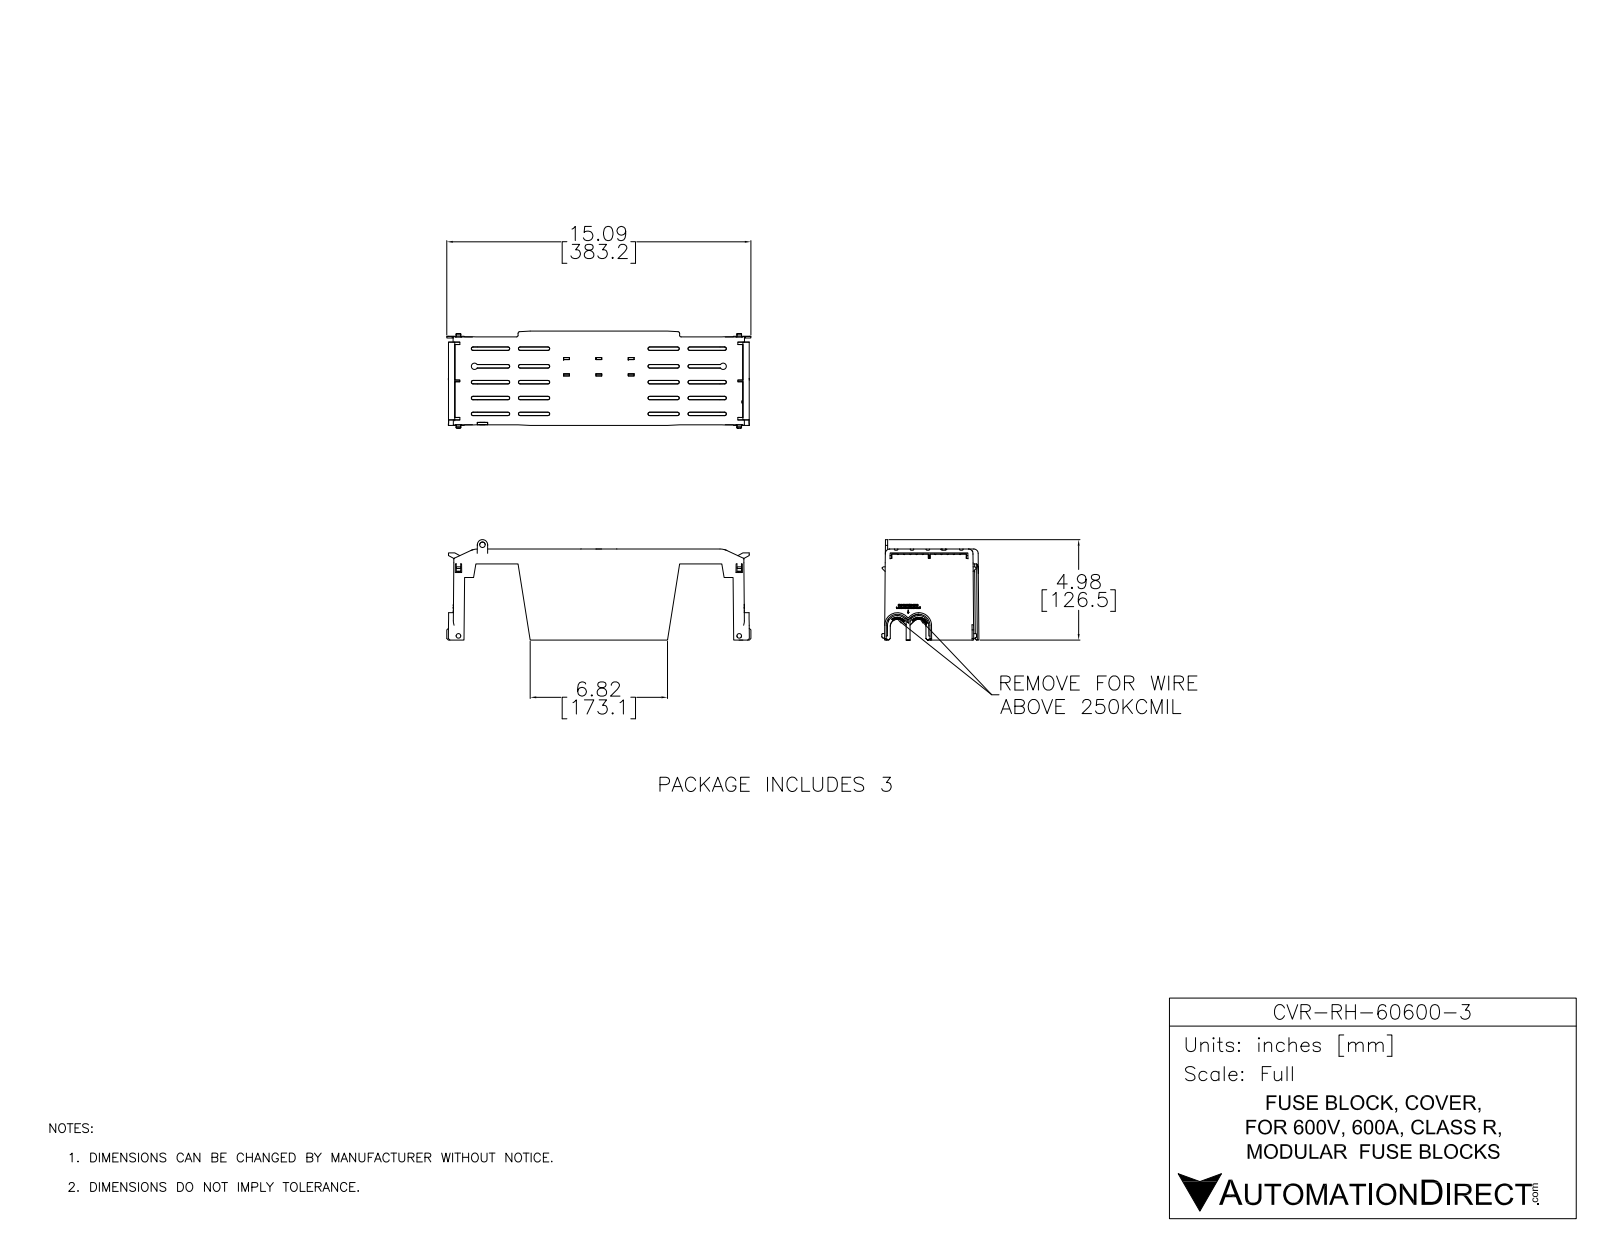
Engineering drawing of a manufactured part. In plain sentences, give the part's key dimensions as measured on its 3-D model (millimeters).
The part is named "CVR-RH-60600-3". Its 3-D file was written by "SolidWorks 2017 (AUTOMOTIVE_DESIGN)". It is 1 solid with 2399 faces: 1630 planar, 123 cylindrical and 646 other. Overall it measures 383.2 by 126.6 by 122.4 millimeters. Its volume is 259 600 cubic millimeters and its surface area 266 800 square millimeters. Round holes: 1 of diameter 7. Round bosses or shafts: 2 of diameter 5.8. Partial cylindrical surfaces (rounded edges, fillets, slot ends): 18 of radius 1, 8 of radius 3, 7 of radius 3.5, 7 of radius 5.5, 4 of radius 2, 4 of radius 9, 4 of radius 12.5, 4 of radius 14. The main face-to-face distances are 2, 6.5, 4.5, 20.2, 5, 8.5, 20.4, 3, 10.2, 40.6.
